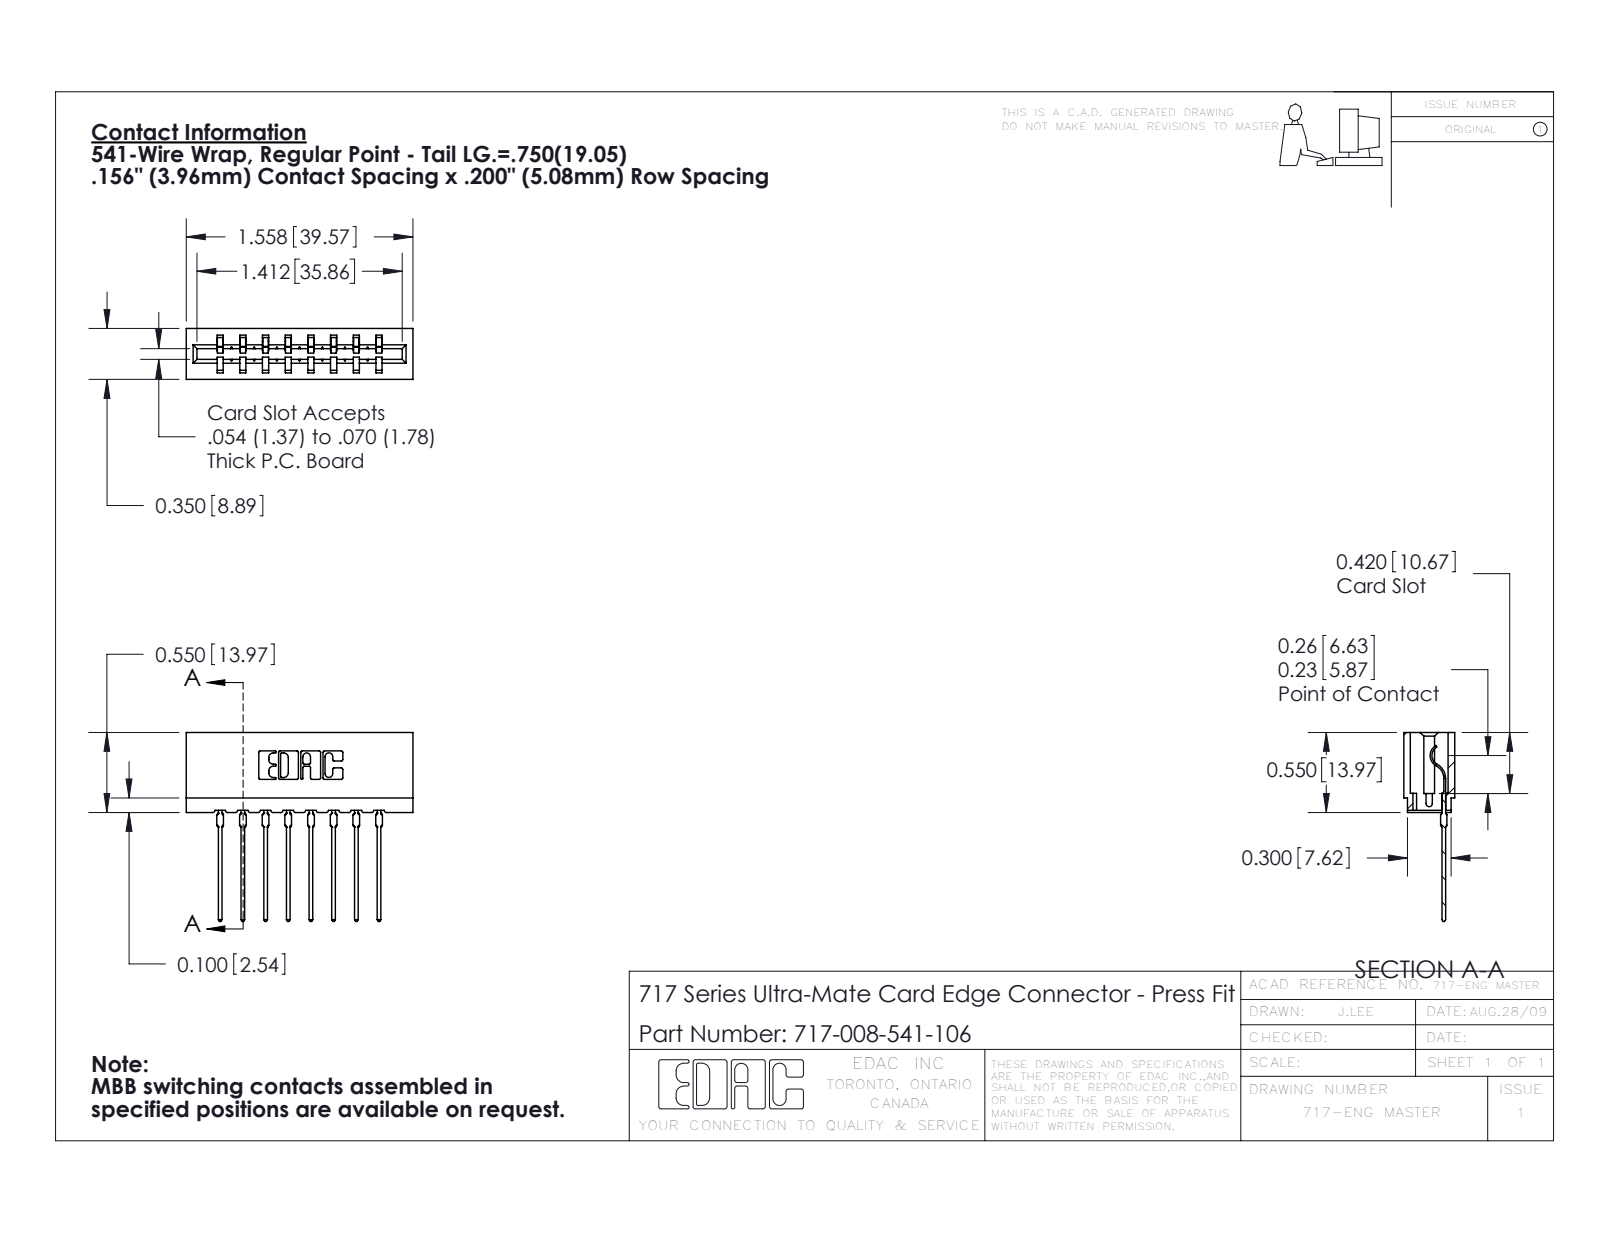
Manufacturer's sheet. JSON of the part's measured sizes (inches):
{"part_name": "717 Part_Insulator Option - 06; 717-008-541-106; 745-292-001_541", "step_written_by": "SolidWorks 2016 (CONFIG_CONTROL_DESIGN)", "units": "inches", "bodies": {"solids": 9, "faces": 998, "planar": 598, "cylindrical": 192, "other": 208}, "overall_size": [1.558, 1.299, 0.35], "volume_in3": 0.215, "surface_area_in2": 7.374, "partial_cylinders_radius": [[0.01, 22], [0.015, 16], [0.021, 16], [0.007, 6], [0.031, 6], [0.005, 4], [0.011, 4], [0.026, 3]], "face_to_face_distances": [0.212, 0.156, 0.138, 0.624, 0.468, 0.198, 0.312, 0.35, 0.042, 0.27]}
